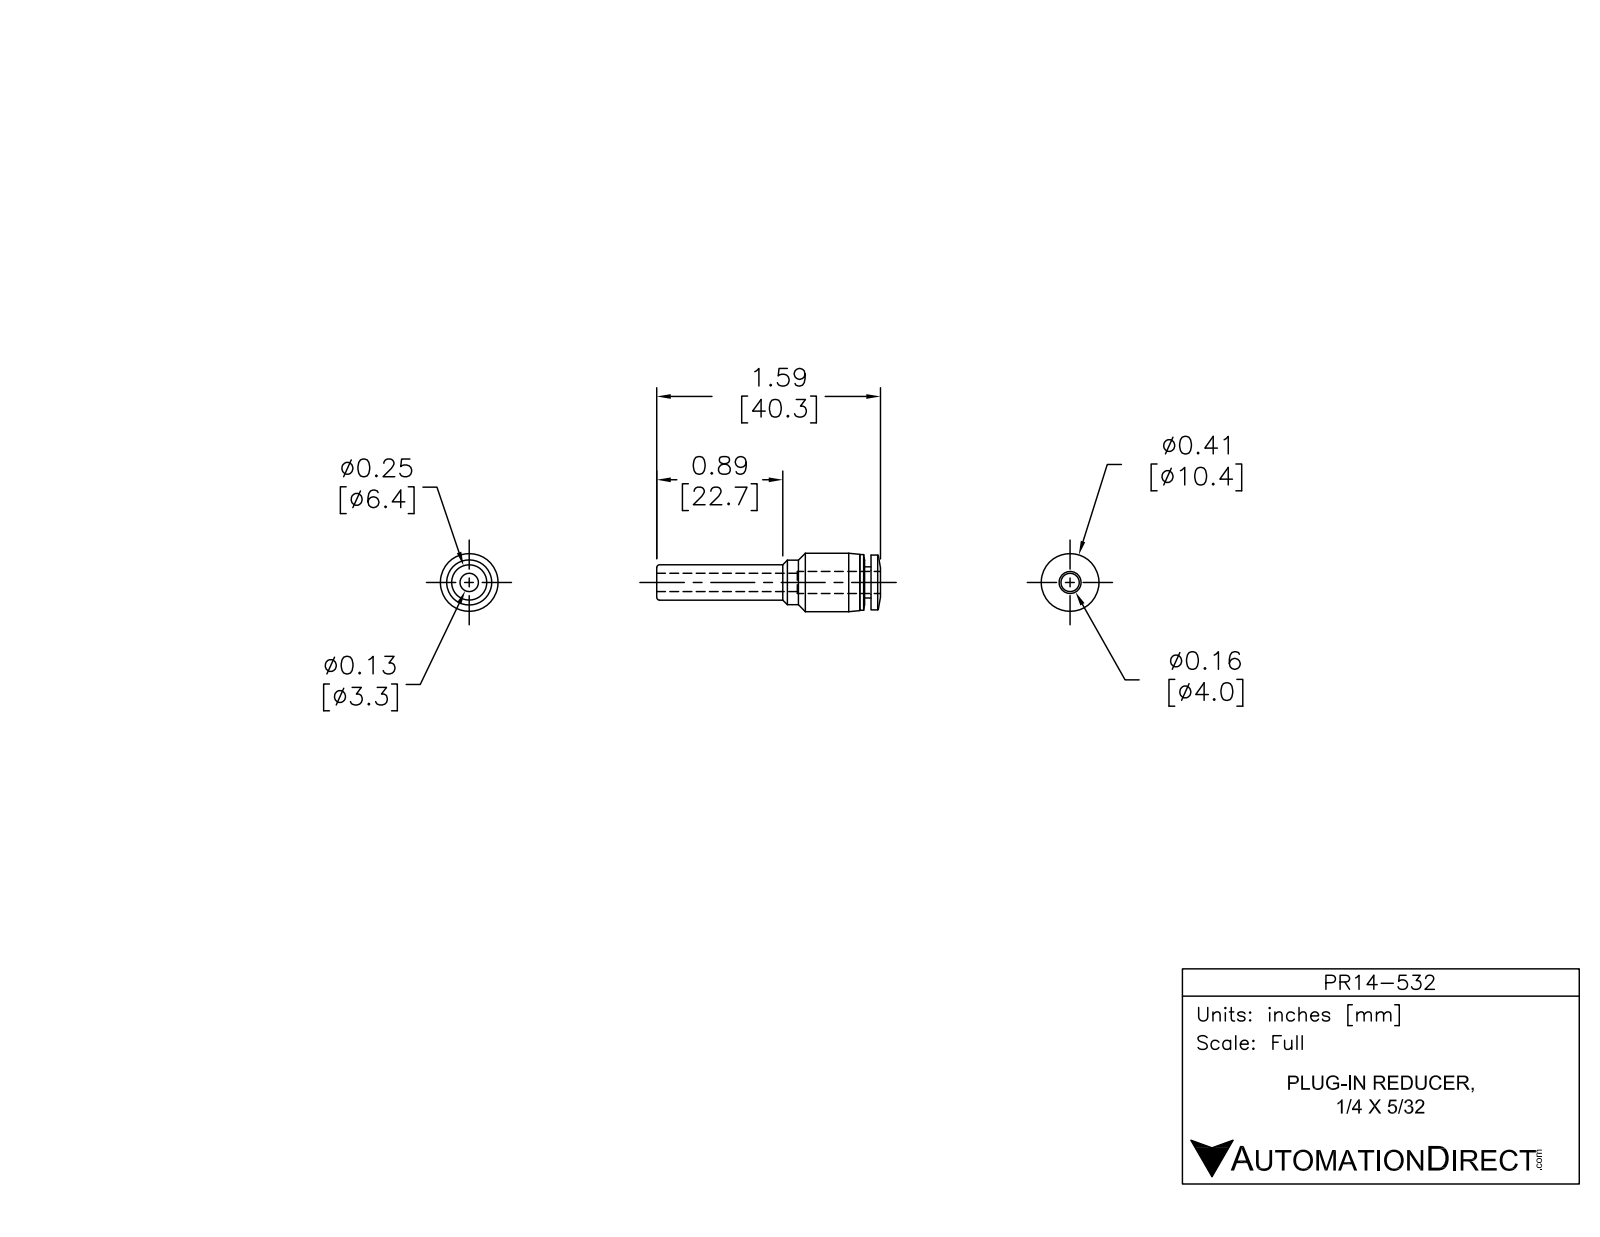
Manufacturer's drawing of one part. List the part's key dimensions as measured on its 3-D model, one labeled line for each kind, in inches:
Part name (STEP PRODUCT): PR14-532
STEP written by: SolidWorks 2015 (AUTOMOTIVE_DESIGN)
Units: inches
Bodies: 1 solid, 39 faces (5 planar, 16 cylindrical, 18 other)
Overall size (bounding box): 1.583 × 0.413 × 0.413
Volume: 0.094 in³ · Surface area: 2.548 in²
Round holes (diameter × count): ⌀0.134 ×1, ⌀0.169 ×1
Round bosses / shafts (diameter × count): ⌀0.413 ×1, ⌀0.394 ×1, ⌀0.388 ×1, ⌀0.315 ×1, ⌀0.25 ×1, ⌀0.22 ×1
Main face-to-face distances: 0.045, 1.47, 1.516, 1, 0.47, 0.516, 1.437, 0.437, 0.033, 0.079
